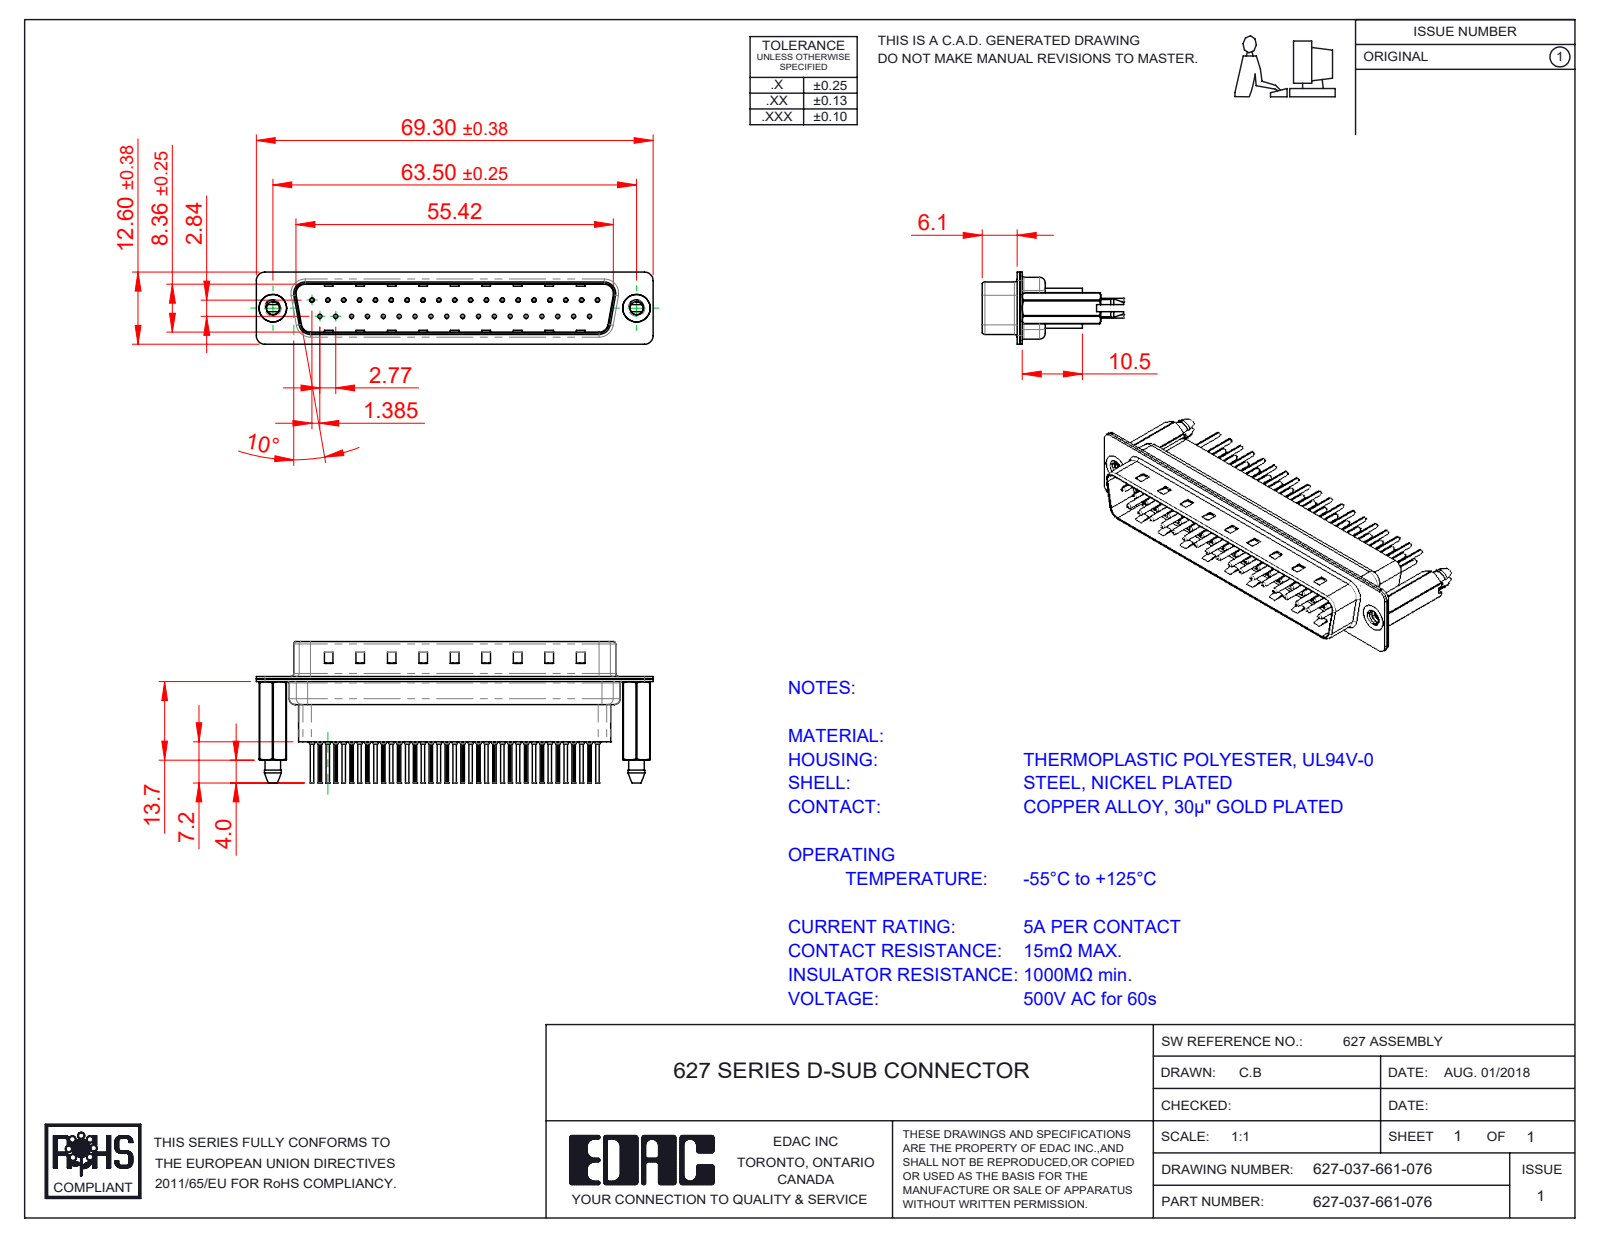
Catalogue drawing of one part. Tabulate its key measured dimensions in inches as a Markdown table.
| quantity | value |
| --- | --- |
| part name | 627 Contact Row 2_61; 627 4-40 Threaded Boardlock_HP61; 627-037-661-076; 627 Housing_37 HP (+3 more) |
| STEP written by | SolidWorks 2020 (CONFIG_CONTROL_DESIGN) |
| units | inches |
| bodies | 42 solids, 4146 faces (1123 planar, 1576 cylindrical, 1447 other) |
| overall size | 2.728 × 0.969 × 0.496 |
| volume | 0.347 in³ |
| surface area | 22.76 in² |
| round holes (diameter × count) | 0.008 × 37, 0.014 × 37, 0.043 × 37, 0.063 × 37, 0.089 × 2, 0.157 × 2, 0.189 × 2 |
| round bosses / shafts (diameter × count) | 0.079 × 37, 0.059 × 37, 0.03 × 37, 0.024 × 37, 0.193 × 2 |
| partial cylindrical surfaces (radius × count) | 0.004 × 74, 0.059 × 18, 0.079 × 12, 0.063 × 10, 0.02 × 8, 0.01 × 4, 0.024 × 4, 0.026 × 4 |
| main face-to-face distances | 0.016, 0.032, 0.377, 0.027, 0.302, 0.018, 0.059, 0.043, 0.318, 0.345 |
| hole center spacings | 0.124, 0.109, 0.218, 0.327, 0.198, 0.398, 0.436, 0.503 |
